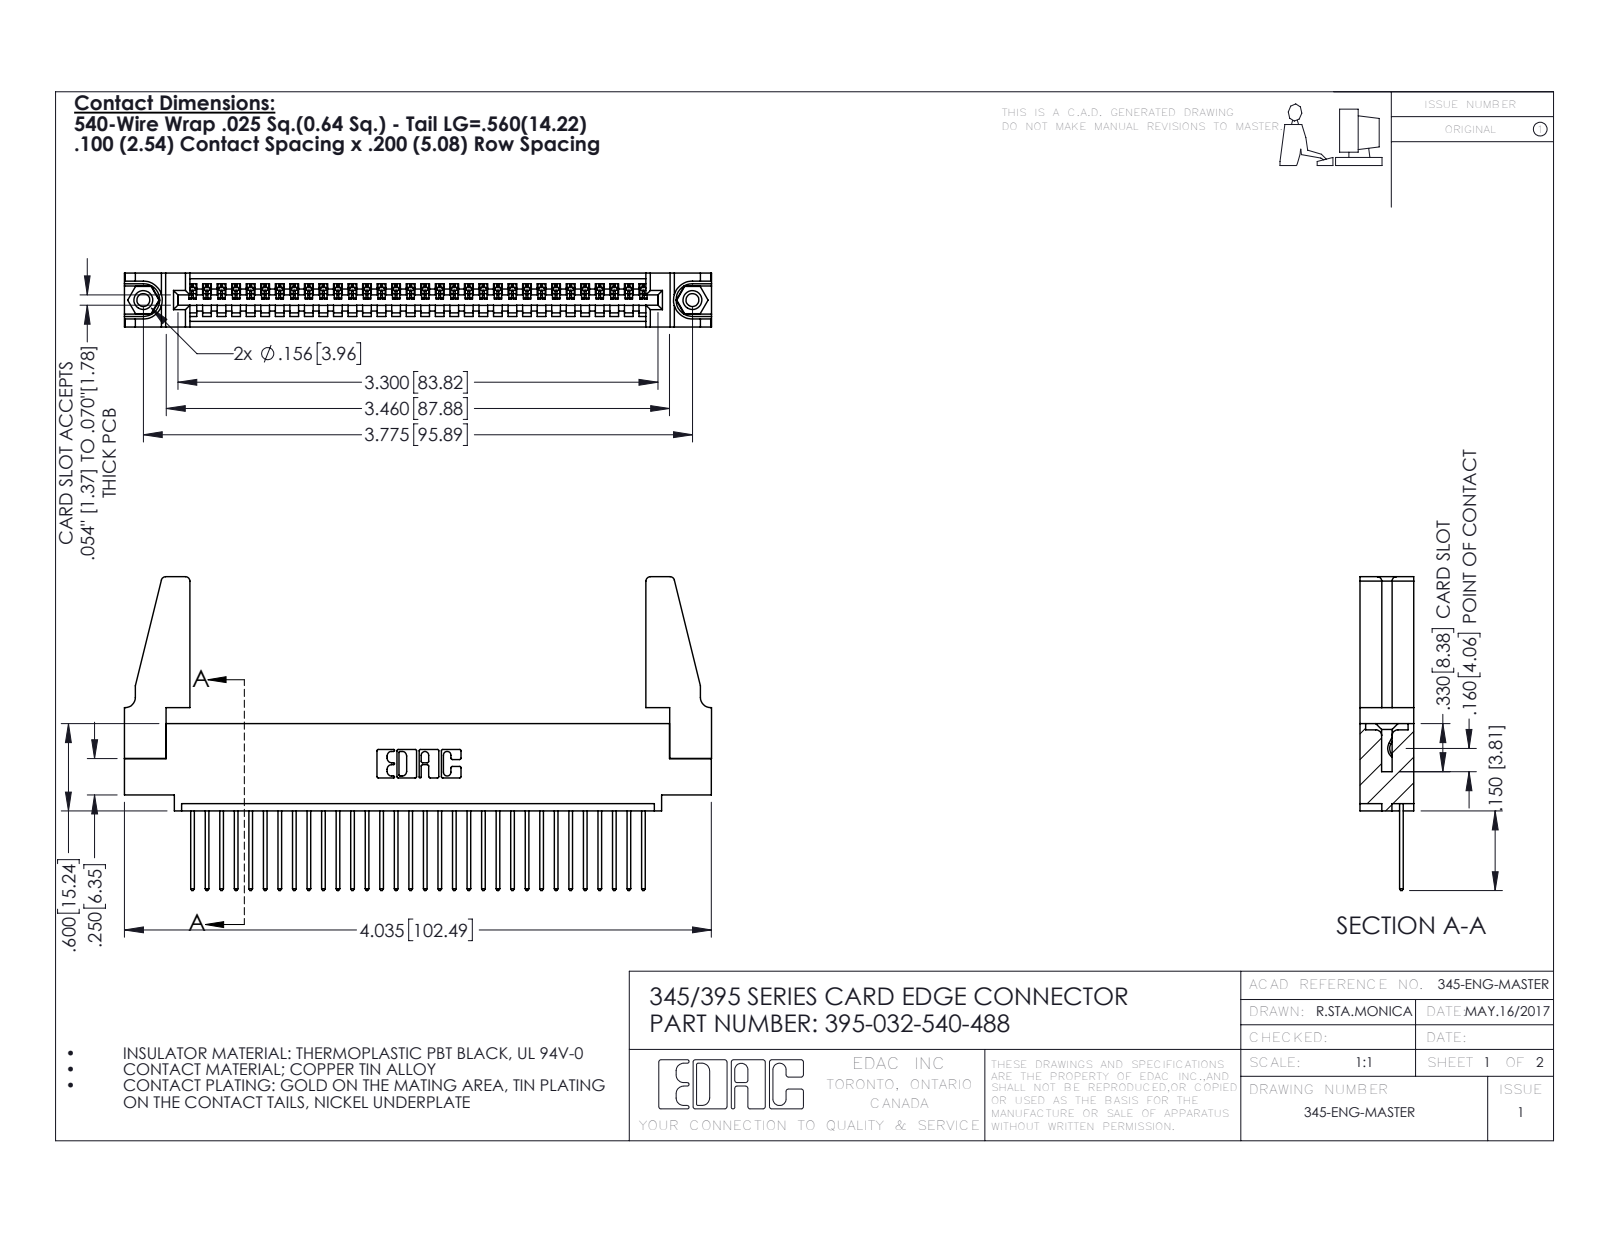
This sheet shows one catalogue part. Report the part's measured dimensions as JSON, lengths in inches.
{"part_name": "345-220-078_345-220-088; 345 Part_0.110 Offset - 0.156 Dia-TH; 345-292-001_345-293-140; 345-250-001_345-250-001-102 (+1 more)", "step_written_by": "SolidWorks 2016 (CONFIG_CONTROL_DESIGN)", "units": "inches", "bodies": {"solids": 37, "faces": 2110, "planar": 1436, "cylindrical": 658, "other": 16}, "overall_size": [4.036, 2.157, 0.37], "volume_in3": 0.786, "surface_area_in2": 25.08, "round_holes": [[0.089, 2], [0.125, 2], [0.156, 2], [0.064, 1]], "round_bosses_or_shafts": [[0.155, 2]], "partial_cylinders_radius": [[0.006, 64], [0.01, 64], [0.01, 22], [0.03, 8], [0.007, 6], [0.031, 6], [0.026, 3], [0.031, 2]], "face_to_face_distances": [0.072, 0.298, 0.37, 0.098, 0.272, 0.025, 0.2, 0.225, 0.149, 0.072], "hole_center_spacings": [0.27, 3.54, 3.775]}
